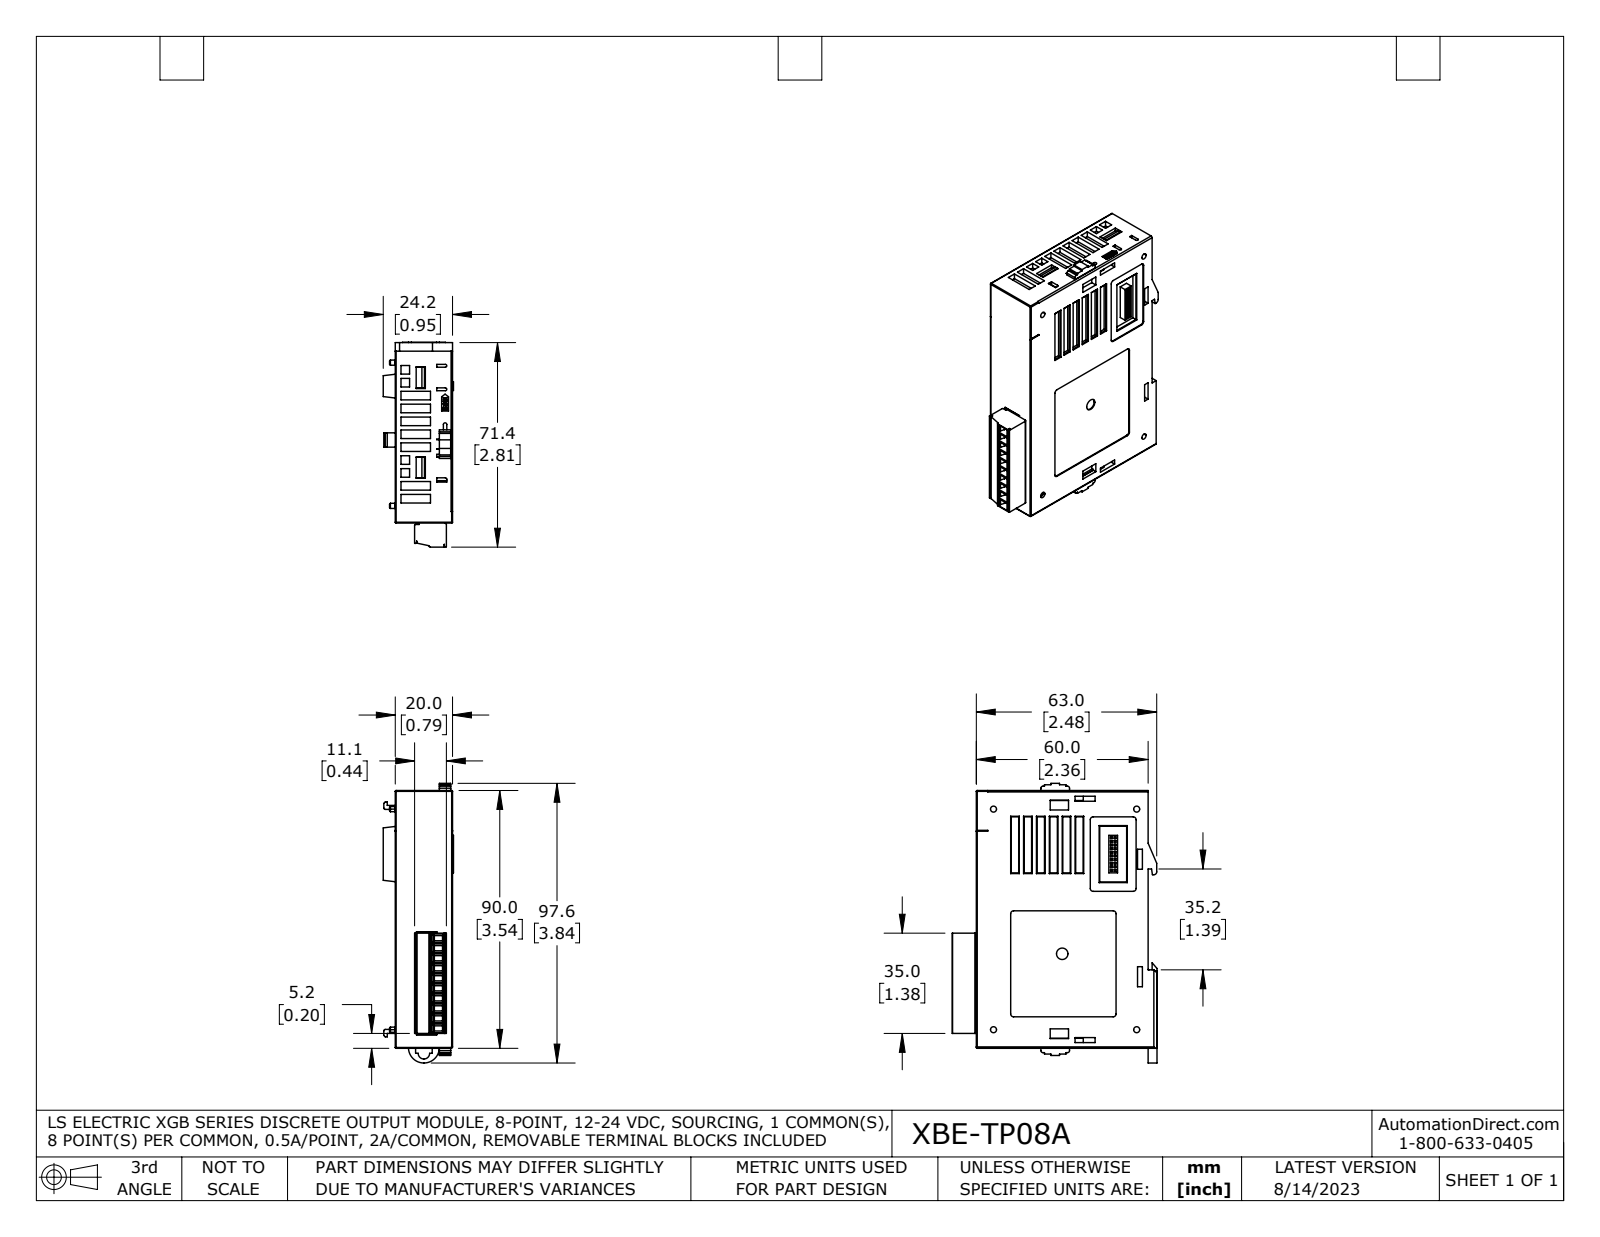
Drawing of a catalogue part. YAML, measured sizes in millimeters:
part_name: "XBE-TP08A nc din clip 6 bad faces cut1 coord"
step_written_by: "SolidWorks 2021 (AUTOMOTIVE_DESIGN)"
units: millimeters
bodies: {solids: 1, faces: 2347, planar: 1755, cylindrical: 404, other: 188}
overall_size: [97.63, 71.5, 24.53]
volume: 107675
surface_area: 29188
round_holes:
  - {diameter: 2.75, count: 10}
  - {diameter: 2.95, count: 10}
  - {diameter: 2.1, count: 4}
  - {diameter: 1.8, count: 2}
  - {diameter: 4, count: 1}
round_bosses_or_shafts:
  - {diameter: 2.8, count: 10}
  - {diameter: 1.8, count: 6}
partial_cylinders:
  - {radius: 0.2, count: 42}
  - {radius: 0.1, count: 40}
  - {radius: 0.3, count: 38}
  - {radius: 0.5, count: 21}
  - {radius: 1, count: 11}
  - {radius: 1.59, count: 10}
  - {radius: 1.8, count: 10}
  - {radius: 0.8, count: 6}
face_to_face_distances: [20, 2, 1, 19.7, 18, 60, 19, 17, 1.7, 0.8]
hole_center_spacings: [3.5, 7, 10.5, 14, 17.5, 21, 24.5, 13.68]
